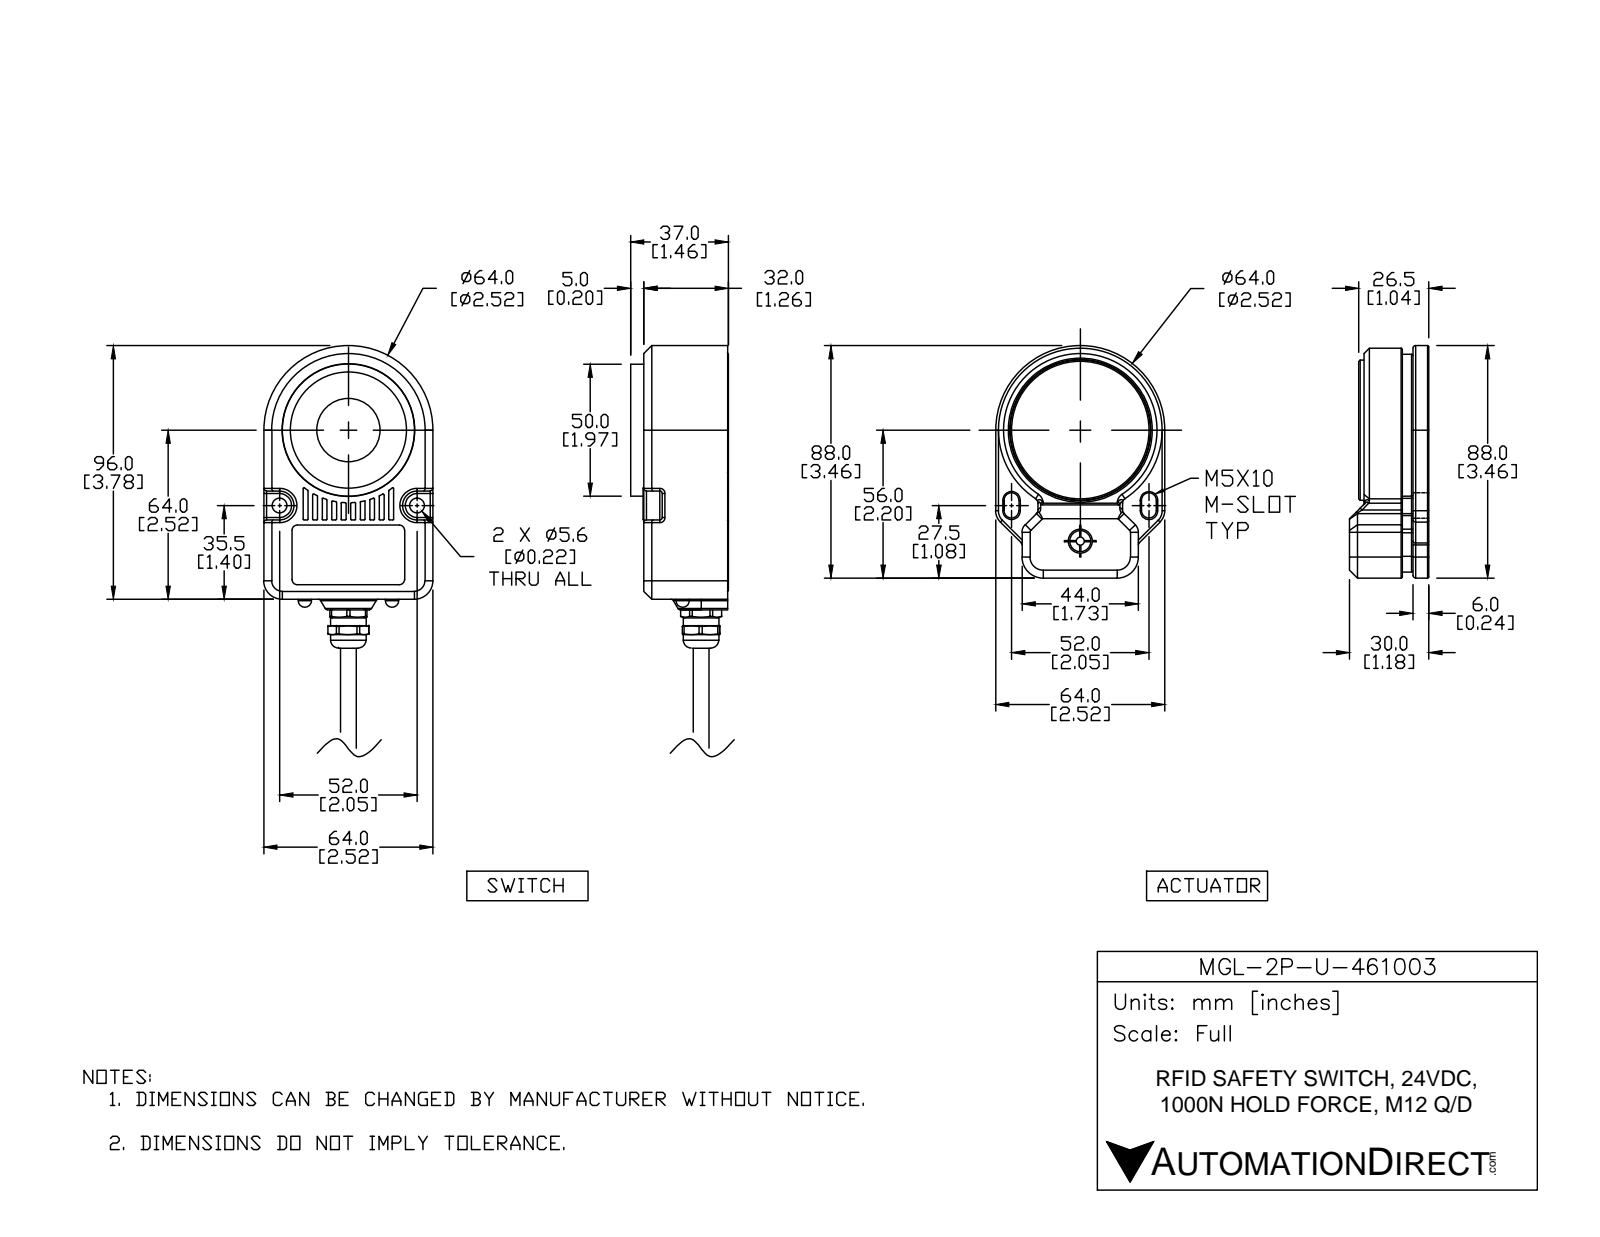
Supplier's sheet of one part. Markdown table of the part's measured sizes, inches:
| quantity | value |
| --- | --- |
| part name | MGL-2P-U-461003; MGL-2P-U-461003_2; MGL-2P-U-461003_1 |
| STEP written by | SolidWorks 2017 (AUTOMOTIVE_DESIGN) |
| units | inches |
| bodies | 17 solids, 1585 faces (431 planar, 674 cylindrical, 480 other) |
| overall size | 7.717 × 2.539 × 2.52 |
| volume | 11.86 in³ |
| surface area | 154.5 in² |
| round holes (diameter × count) | 0.157 × 6, 0.315 × 6, 0.094 × 4, 0.197 × 4, 0.079 × 2, 0.13 × 2, 0.22 × 2, 0.354 × 2, 0.413 × 2, 0.669 × 2, 0.252 × 1, 0.256 × 1 |
| round bosses / shafts (diameter × count) | 0.02 × 4, 0.079 × 3, 0.472 × 2, 0.236 × 2, 0.228 × 2, 0.213 × 2, 0.146 × 2, 2.441 × 1 |
| partial cylindrical surfaces (radius × count) | 0.02 × 180, 0.039 × 60, 0.012 × 39, 0.079 × 20, 0.024 × 7, 0.157 × 6, 0.236 × 5, 0.315 × 5 |
| main face-to-face distances | 0.098, 0.236, 2.303, 0.413, 0.65, 2.539, 0.118, 2.421, 0.394, 0.315 |
| hole center spacings | 0.706, 0.768, 1.086, 0.669, 1.024, 1.159, 0.173, 0.346 |
